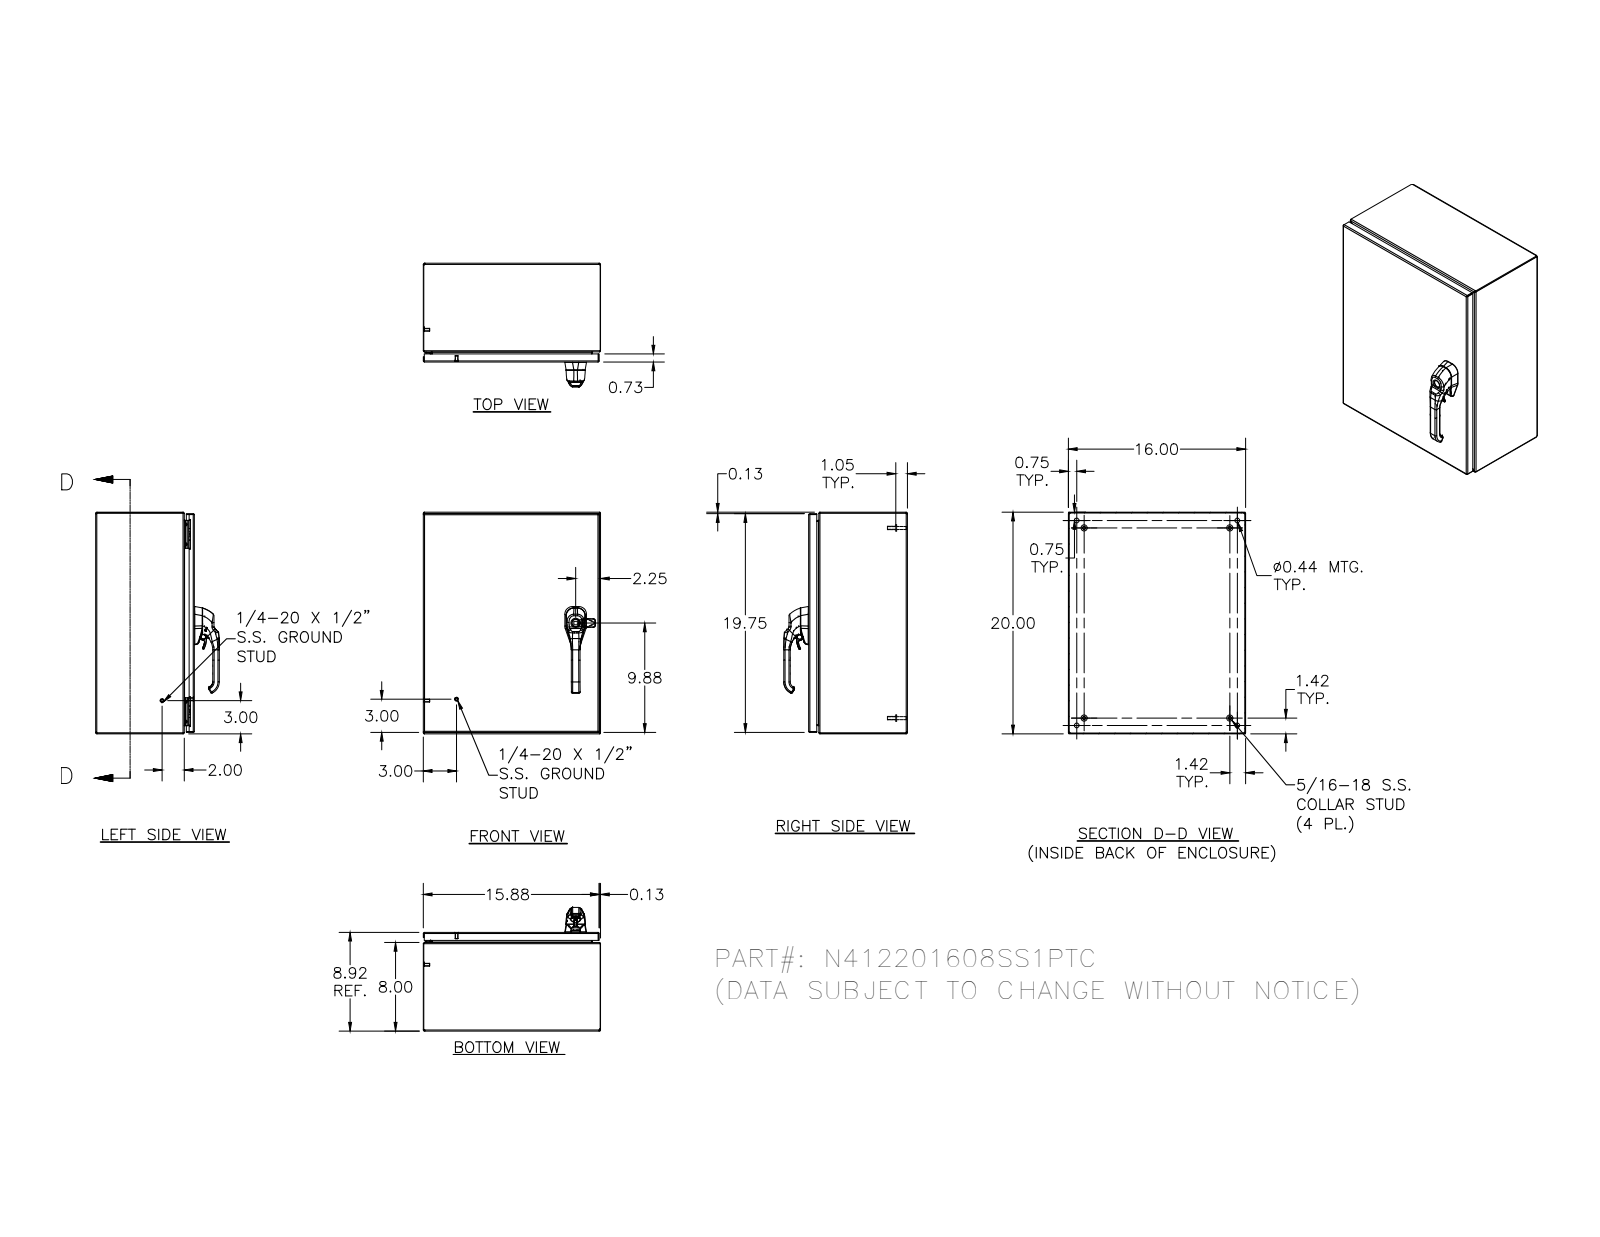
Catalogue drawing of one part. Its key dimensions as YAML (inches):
part_name: "N412201608SS1PTC; N412201608SS1PTCBKP; N4122016SS1PTCLID; HFW328176 (+8 more)"
step_written_by: "Autodesk Inventor 2012 (AUTOMOTIVE_DESIGN)"
units: inches
bodies: {solids: 41, faces: 2782, planar: 882, cylindrical: 1035, other: 865}
overall_size: [20, 16, 11.166]
volume: 107.9
surface_area: 2836
round_holes:
  - {diameter: 0.093, count: 4}
  - {diameter: 0.152, count: 4}
  - {diameter: 0.167, count: 4}
  - {diameter: 0.172, count: 4}
  - {diameter: 0.188, count: 4}
  - {diameter: 0.437, count: 4}
  - {diameter: 0.213, count: 3}
  - {diameter: 0.281, count: 3}
  - {diameter: 0.156, count: 2}
  - {diameter: 0.315, count: 2}
  - {diameter: 0.402, count: 2}
  - {diameter: 0.413, count: 2}
round_bosses_or_shafts:
  - {diameter: 0.25, count: 10}
  - {diameter: 0.563, count: 4}
  - {diameter: 0.36, count: 4}
  - {diameter: 0.32, count: 4}
  - {diameter: 0.3, count: 4}
  - {diameter: 0.275, count: 4}
  - {diameter: 0.256, count: 4}
  - {diameter: 0.164, count: 4}
partial_cylinders:
  - {radius: 0.02, count: 174}
  - {radius: 0.012, count: 101}
  - {radius: 0.031, count: 30}
  - {radius: 0.05, count: 26}
  - {radius: 0.019, count: 21}
  - {radius: 0.105, count: 20}
  - {radius: 0.016, count: 18}
  - {radius: 0.079, count: 14}
face_to_face_distances: [0.074, 8.843, 15.926, 8.917, 8.769, 19.926, 15.852, 16, 19.852, 20]
hole_center_spacings: [15.996, 0.017, 0.66, 15.283, 16.004, 16.656, 0.019, 0.5]
